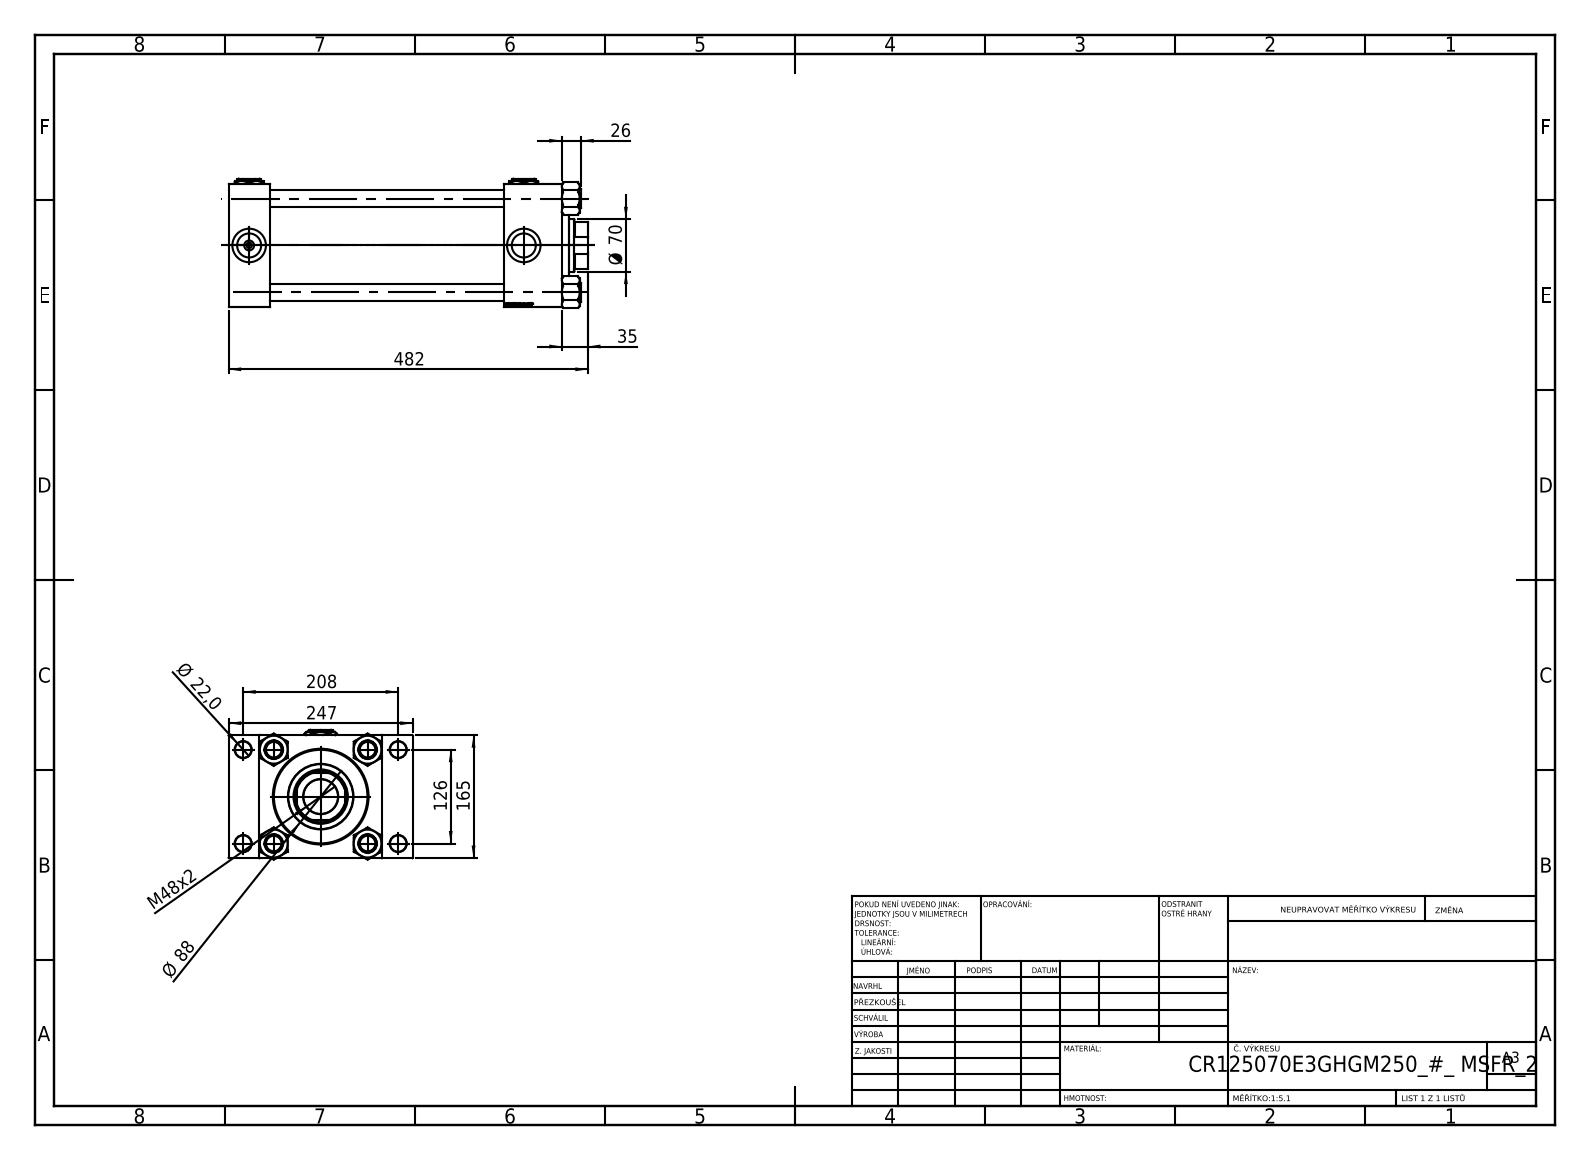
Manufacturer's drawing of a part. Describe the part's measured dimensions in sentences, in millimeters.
The part is named "V215CR_TYCINKA_E; Zatka_pro_OIL_PORT; V215CR_VCP_E; V215CR_E_Body (+2 more)". Its 3-D file was written by "SolidWorks 2019 (CONFIG_CONTROL_DESIGN)". It is 13 solids with 1284 faces: 593 planar, 97 cylindrical and 594 other. Overall it measures 482 by 247 by 174.07 millimeters. Its volume is 6 770 000 cubic millimeters and its surface area 890 172 square millimeters. Round holes: 8 of diameter 22, 4 of diameter 32.24, 4 of diameter 45, 3 of diameter 7, 1 of diameter 46.5, 1 of diameter 70, 1 of diameter 73, 1 of diameter 96, 1 of diameter 125, 1 of diameter 125.5. Round bosses or shafts: 4 of diameter 25, 1 of diameter 131, 1 of diameter 88. Partial cylindrical surfaces (rounded edges, fillets, slot ends): 1 of radius 34. The main face-to-face distances are 55, 165, 447, 392, 41, 78, 369, 314, 206, 418.3. The hole center spacings are 41.05, 89.02, 121.59, 125.9, 132.47, 166.95, 209.13, 126.
